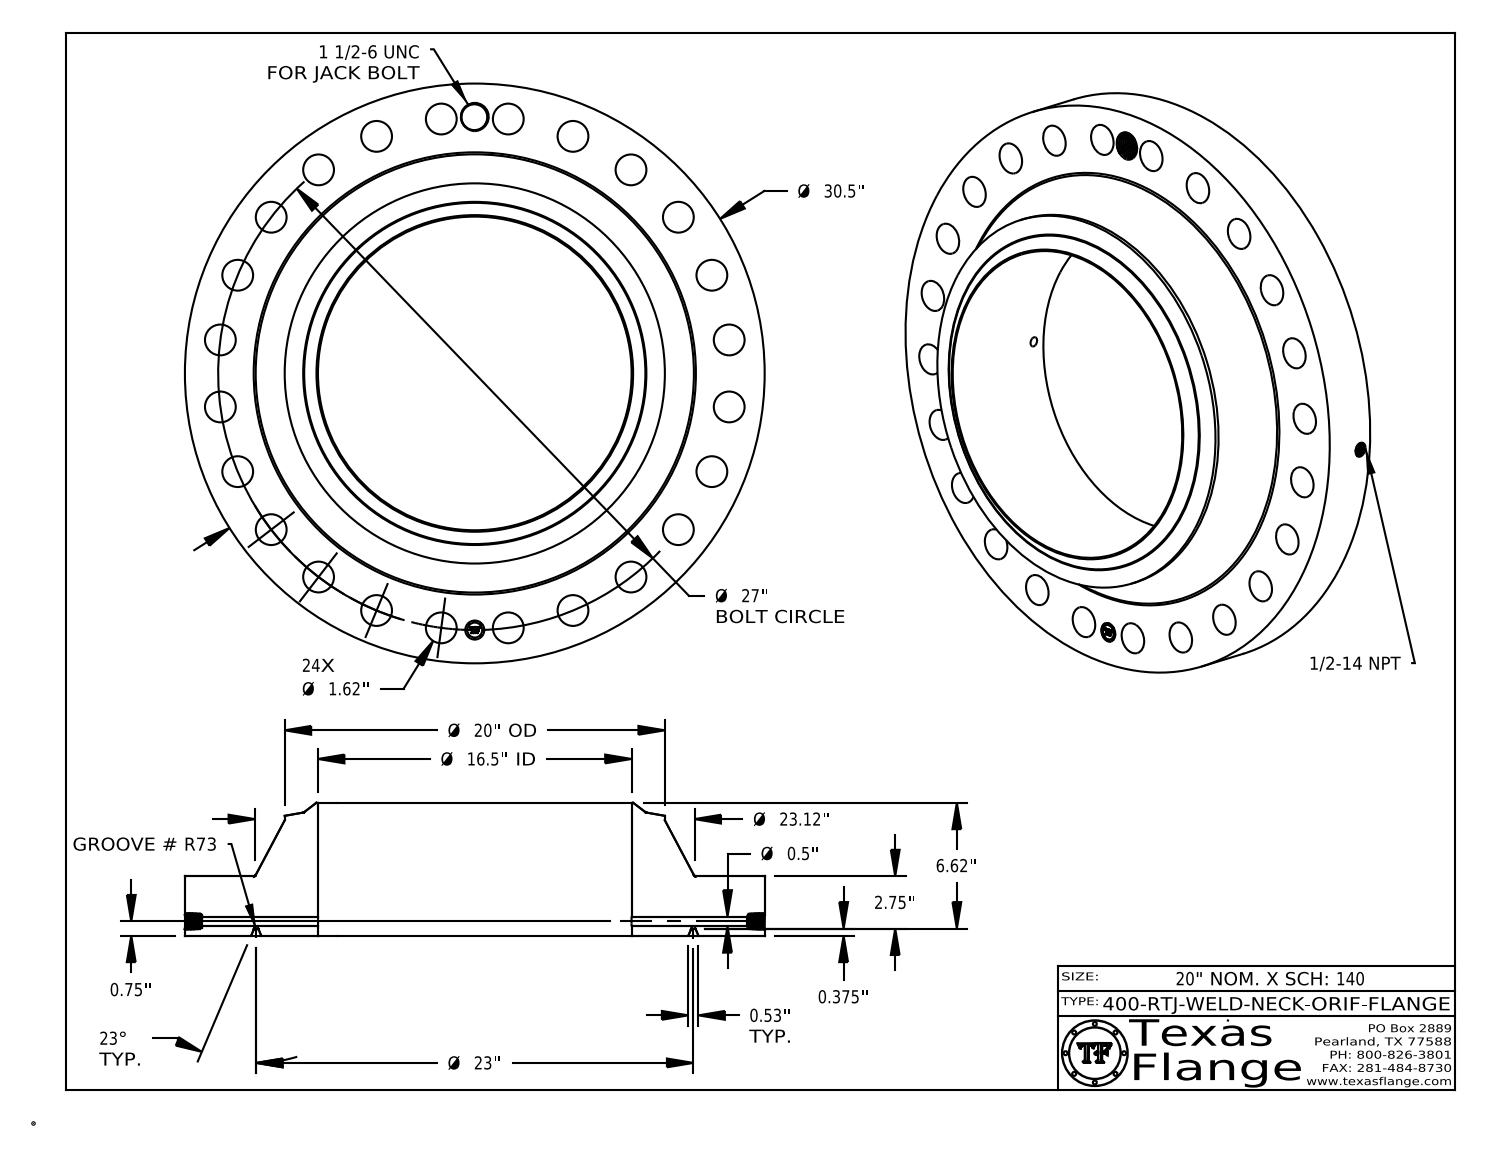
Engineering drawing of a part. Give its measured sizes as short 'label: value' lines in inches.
name: 400-RTJ-WELD-NECK
written by: CATIA V5 STEP AP214 (AUTOMOTIVE_DESIGN)
unit: in
bodies: 1 solid, 835 faces (370 planar, 131 cylindrical, 334 other)
size: 30.5 × 30.5 × 6.995
volume: 1 937 in³; area: 2 198 in²
holes: 24× ⌀1.62, 1× ⌀0.5, 1× ⌀0.672, 1× ⌀1, 1× ⌀1.344, 1× ⌀16.5
bosses: 8× ⌀0.061, 1× ⌀30.5, 1× ⌀20, 1× ⌀0.788
face distances: 3.125, 0.375, 2.75, 6.995, 6.62, 3.87, 0.015, 3.11, 2.735, 3.885
hole spacings: 13.5, 23.383, 24.945, 21.42, 3.524, 6.988, 19.092, 26.08
